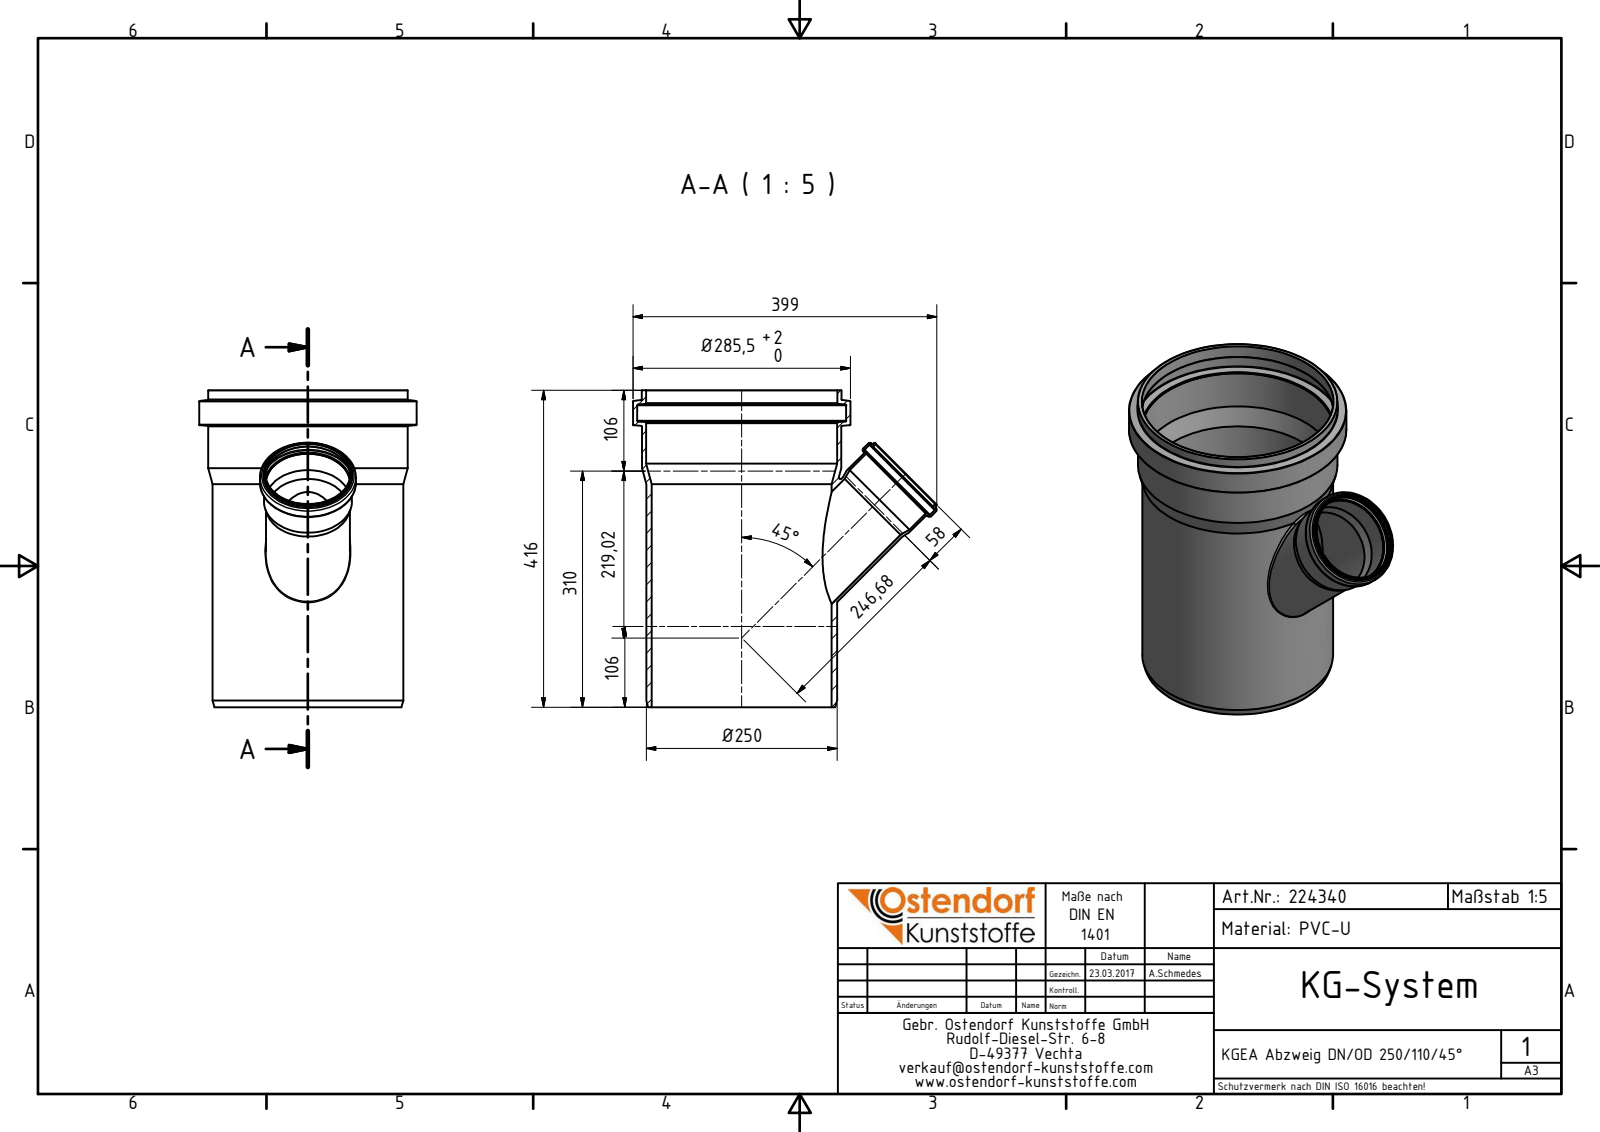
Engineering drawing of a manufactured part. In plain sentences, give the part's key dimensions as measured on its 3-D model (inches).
The part is named "224340 KGEA Abzweig DN_OD 250_110_45°". Its 3-D file was written by "Autodesk Inventor 2016 (AUTOMOTIVE_DESIGN)". It is 1 solid with 58 faces: 5 planar, 18 cylindrical and 35 other. Overall it measures 16.378 by 15.709 by 11.24 inches. Its volume is 141.6 cubic inches and its surface area 1 193 square inches. Round holes: 2 of diameter 4.37, 1 of diameter 4.087, 1 of diameter 4.358, 1 of diameter 4.768, 1 of diameter 9.303, 1 of diameter 9.874, 1 of diameter 9.886, 1 of diameter 10.807. Round bosses or shafts: 1 of diameter 11.24, 1 of diameter 10.319, 1 of diameter 10.307, 1 of diameter 9.862, 1 of diameter 4.957, 1 of diameter 4.559, 1 of diameter 4.547, 1 of diameter 4.339. The main face-to-face distances are 16.378, 14.676, 1.702, 0.717.
